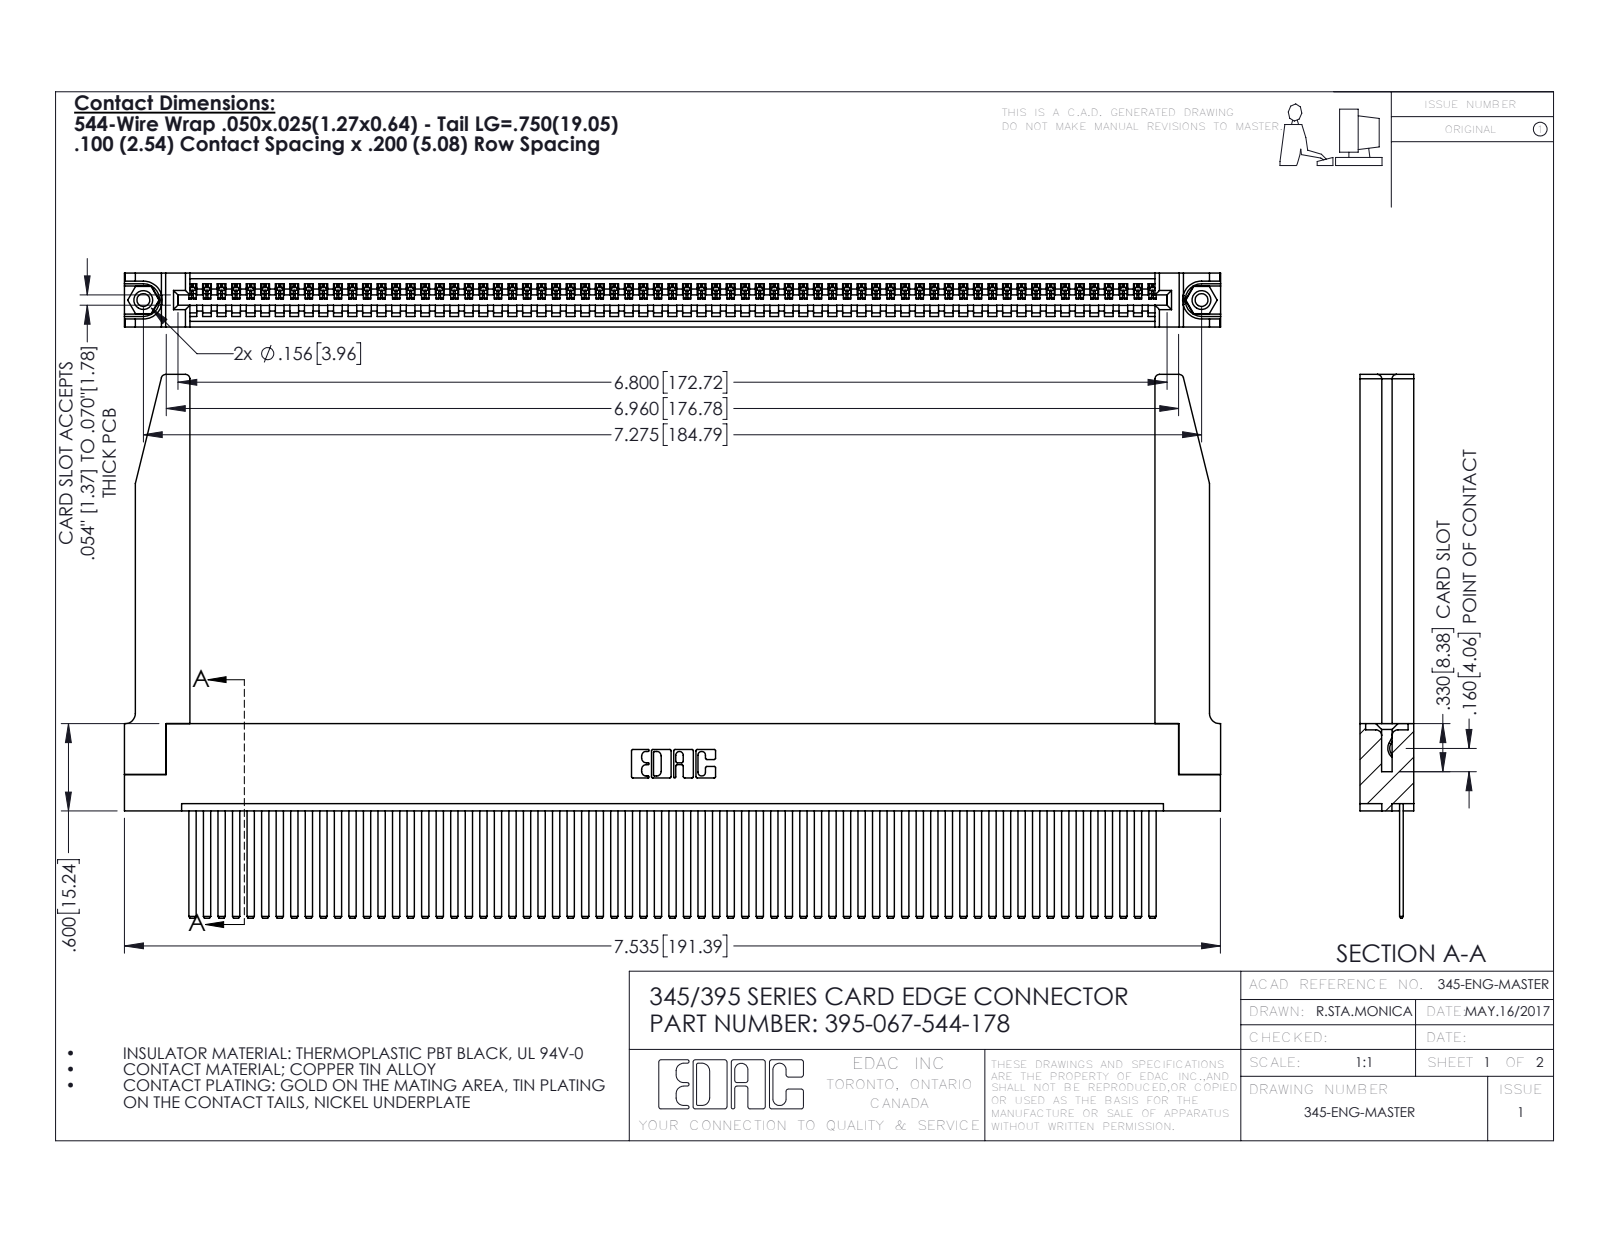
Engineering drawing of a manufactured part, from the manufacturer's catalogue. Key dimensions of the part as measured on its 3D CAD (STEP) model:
Part name (STEP PRODUCT): 395-067-544-178; 345-292-001_345-293-144; 345-220-078_345-220-078; 345 Part_Flush Mounting Lugs - 0.156 Dia-TH (+1 more)
STEP written by: SolidWorks 2016 (CONFIG_CONTROL_DESIGN)
Units: inches
Bodies: 72 solids, 3844 faces (2634 planar, 1158 cylindrical, 52 other)
Overall size (bounding box): 7.536 × 3.737 × 0.37
Volume: 1.643 in³ · Surface area: 54.22 in²
Round holes (diameter × count): ⌀0.089 ×2, ⌀0.125 ×2, ⌀0.156 ×2, ⌀0.064 ×1
Round bosses / shafts (diameter × count): ⌀0.155 ×2
Partial cylindrical surfaces — rounded edges, fillets, slot ends (radius × count): R0.006 ×134, R0.01 ×22, R0.03 ×8, R0.007 ×6, R0.031 ×6, R0.026 ×3, R0.031 ×2, R0.04 ×2
Main face-to-face distances: 0.072, 0.298, 0.37, 0.098, 0.272, 0.025, 0.2, 0.225, 0.149, 0.148
Hole centre spacings: 0.27, 7.039, 7.275
